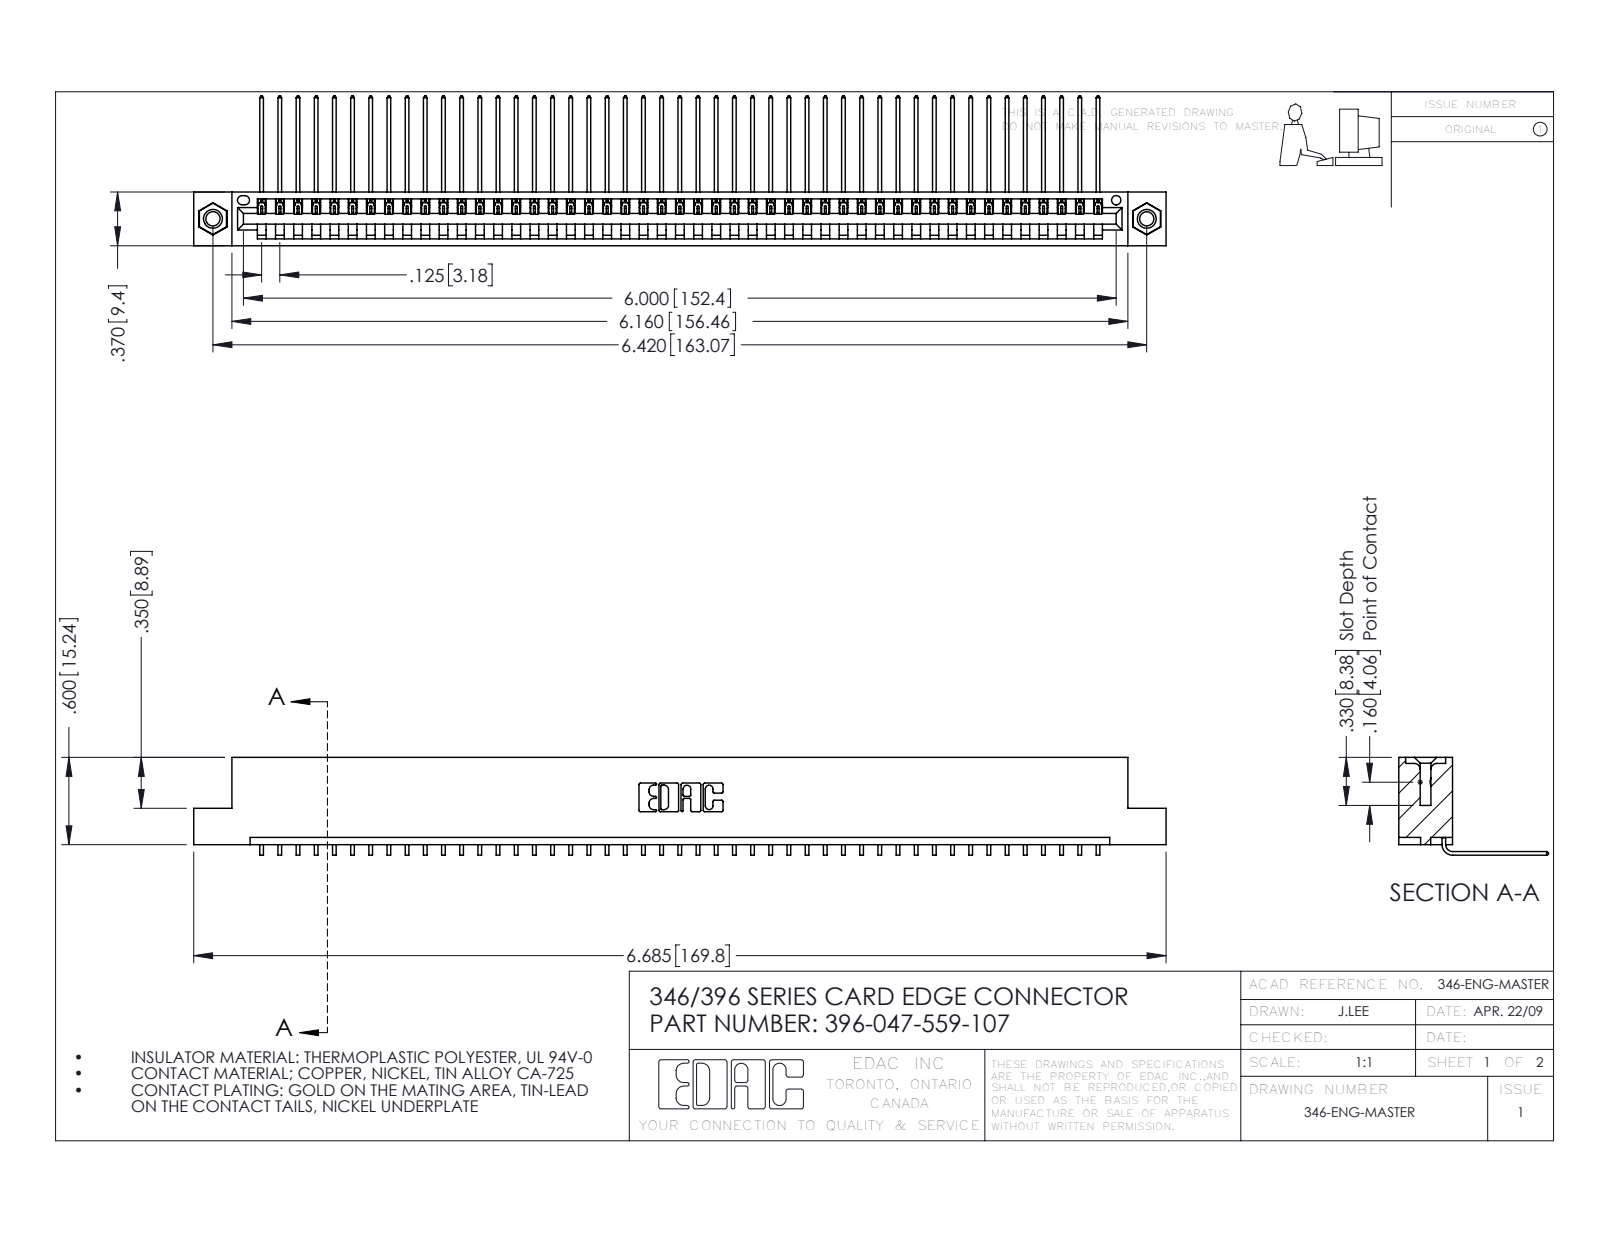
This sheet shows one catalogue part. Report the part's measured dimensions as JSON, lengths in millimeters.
{"part_name": "345-250-001_345-250-005-103; 346 Part_Flush Mounting Lugs - 0.156 Dia-TI; 396-047-559-107; 345-292-001_558 559 Tail - 1", "step_written_by": "SolidWorks 2016 (CONFIG_CONTROL_DESIGN)", "units": "millimeters", "bodies": {"solids": 50, "faces": 3002, "planar": 2082, "cylindrical": 904, "other": 16}, "overall_size": [169.8, 26.2, 17.1], "volume_mm3": 16440, "surface_area_mm2": 21560, "round_holes": [[2.5, 2], [3.2, 2], [4, 2], [1.6, 1]], "round_bosses_or_shafts": [[3.9, 2]], "partial_cylinders_radius": [[0.2, 94], [0.3, 22], [0.2, 6], [0.8, 6], [0.7, 3], [0.8, 2], [1, 2], [0.4, 1]], "face_to_face_distances": [1.2, 8.2, 9.4, 0.6, 6.4, 1.8, 7.6, 3.8, 5.6, 2.5], "hole_center_spacings": [6.2, 157.8, 163.1]}
